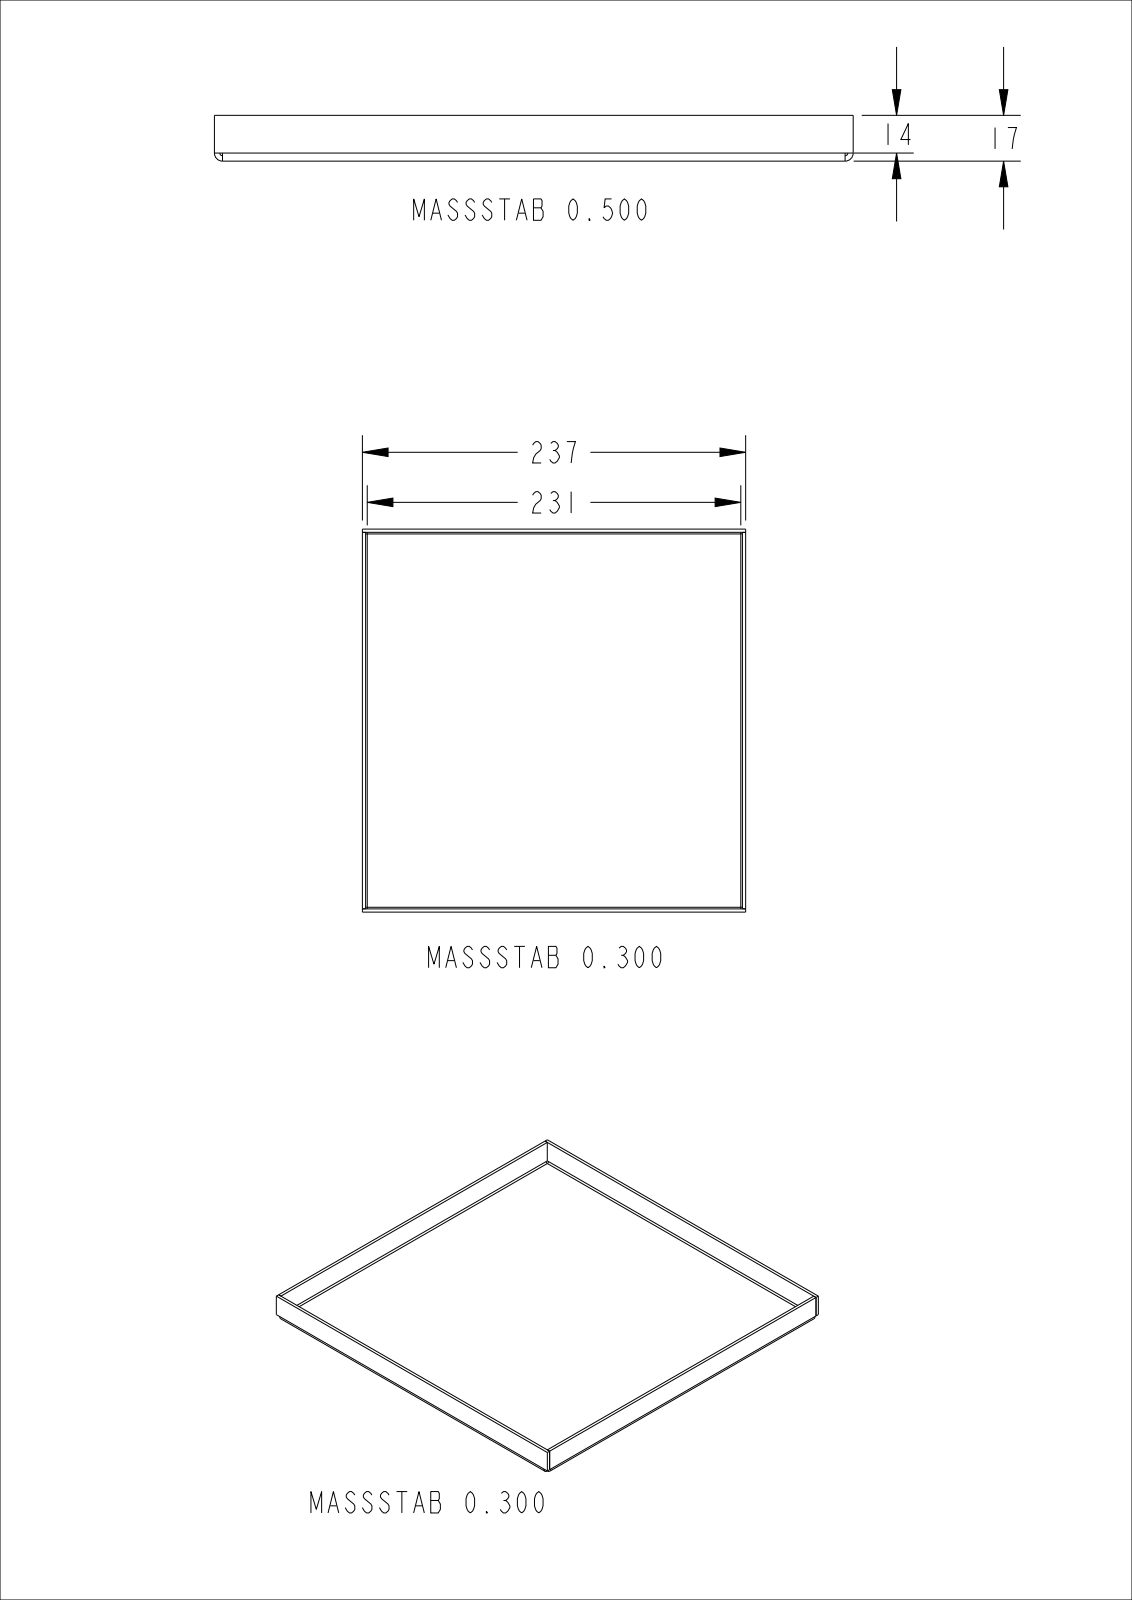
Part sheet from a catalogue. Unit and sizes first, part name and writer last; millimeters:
Units: millimetres
Overall size (bounding box): 237 × 237 × 17
Partial cylindrical surfaces — rounded edges, fillets, slot ends (radius × count): R1 ×4, R3 ×4
Main face-to-face distances: 2, 235, 237, 233, 17, 15, 2.05, 234.95, 232.95, 3
Volume: 138 842 mm³ · Surface area: 141 028 mm²
Bodies: 1 solid, 46 faces (38 planar, 8 cylindrical, 0 other)
Part name (STEP PRODUCT): T-00610; T-00866_ASM; T-00878_ASM
STEP written by: CREO PARAMETRIC BY PTC INC, 2022024 (AUTOMOTIVE_DESIGN)
